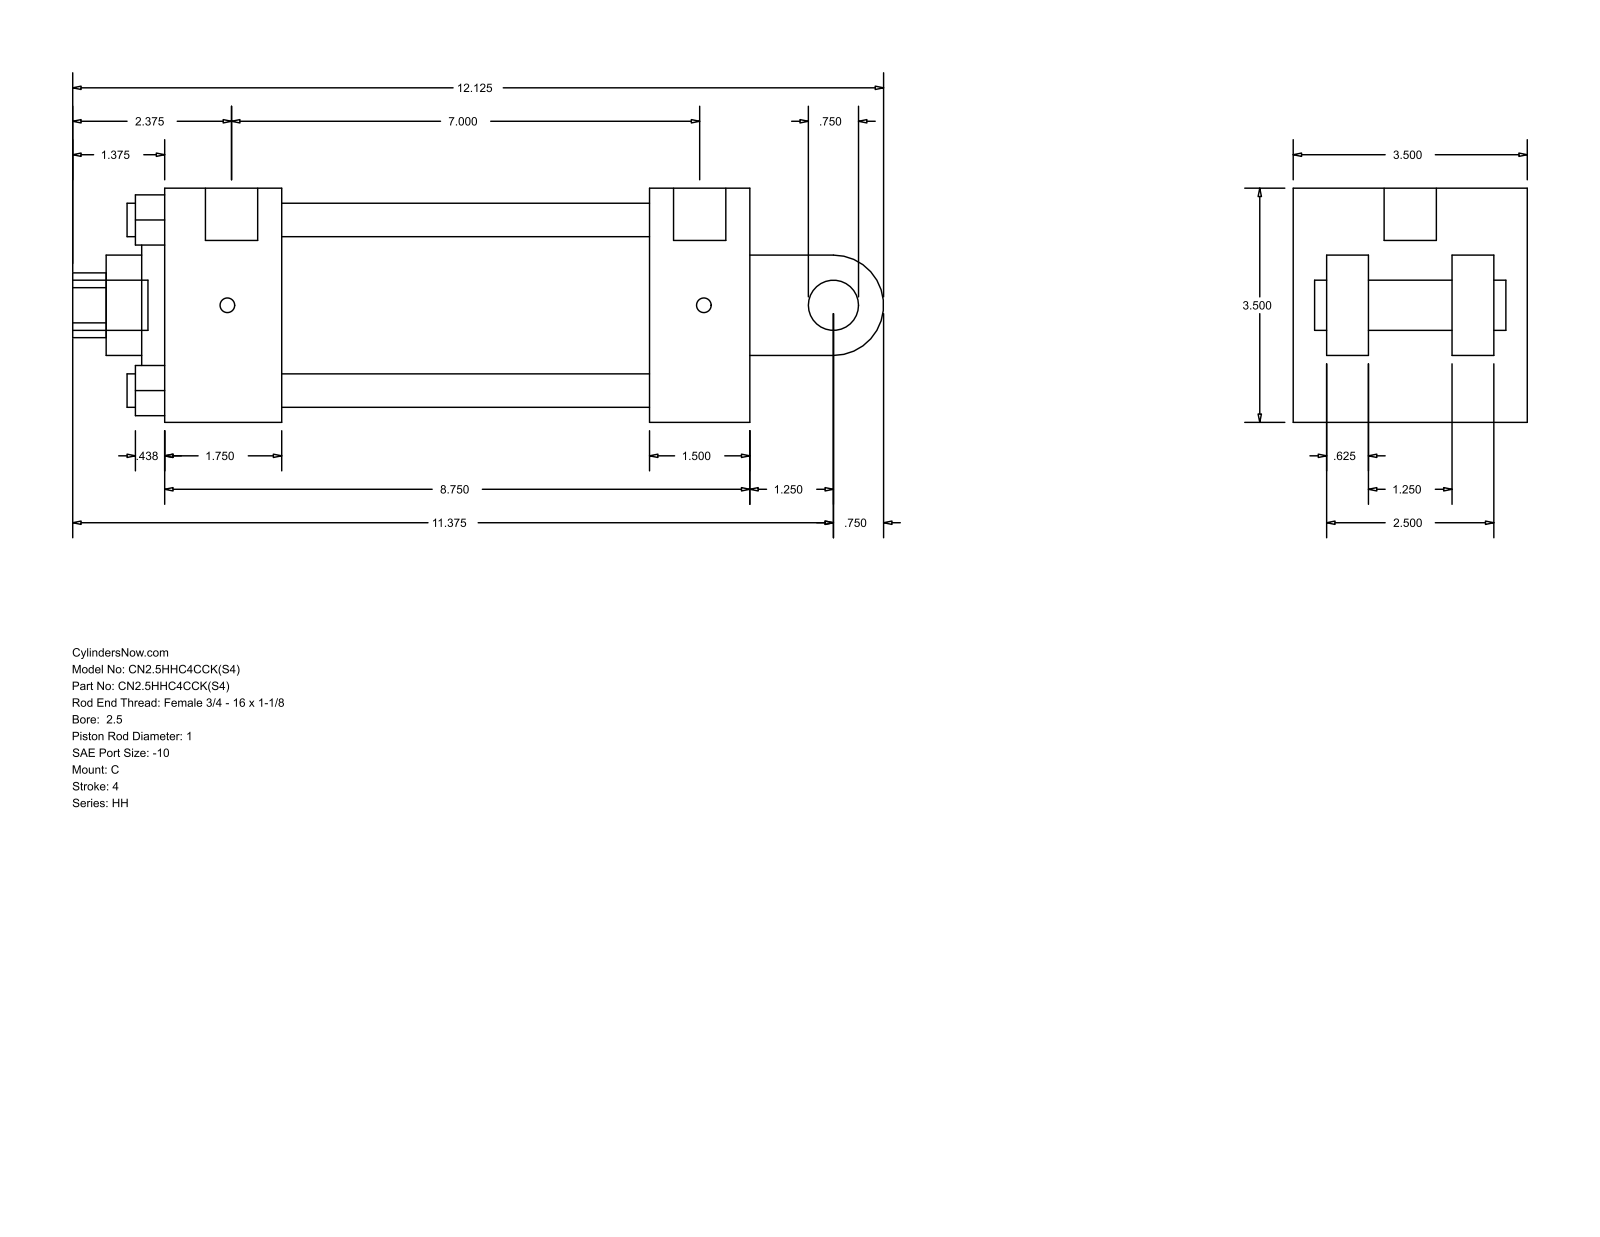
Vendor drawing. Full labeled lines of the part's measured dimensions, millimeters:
Part name (STEP PRODUCT): HH_C__0250_1
STEP written by: GSSL Pune (CONFIG_CONTROL_DESIGN)
Units: millimetres
Bodies: 0 solids, 101 faces (71 planar, 30 cylindrical, 0 other)
Overall size (bounding box): 307.98 × 88.9 × 88.9
Round holes (diameter × count): ⌀12.7 ×4, ⌀5.56 ×2, ⌀19.84 ×1, ⌀25.4 ×1, ⌀38.1 ×1, ⌀60.33 ×1, ⌀73.03 ×1
Round bosses / shafts (diameter × count): ⌀19.05 ×2, ⌀5.56 ×2, ⌀19.84 ×1
Partial cylindrical surfaces — rounded edges, fillets, slot ends (radius × count): R12.29 ×1, R19.05 ×1
Main face-to-face distances: 88.9, 222.26, 63.5, 15.87, 184.15, 38.11, 44.46, 139.69, 177.8, 12.7
Hole centre spacings: 45.79, 64.76, 91.58, 1.59
